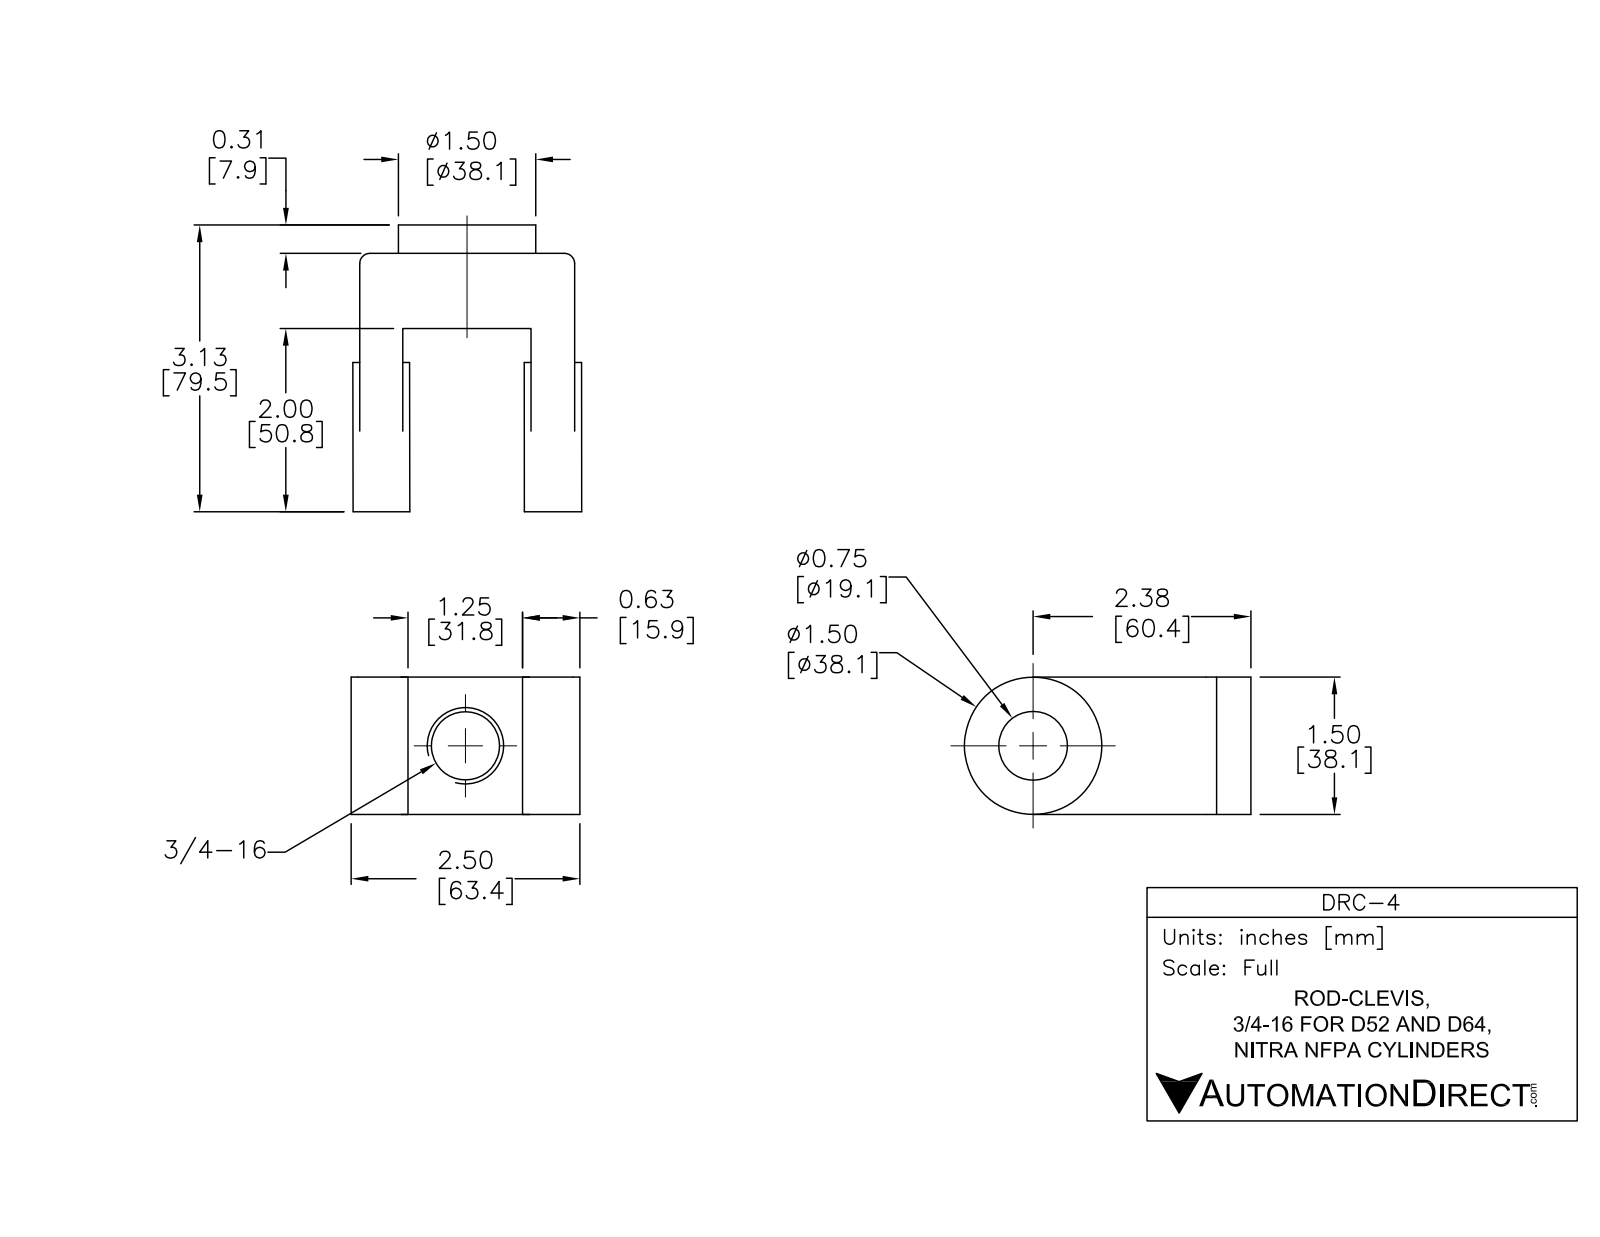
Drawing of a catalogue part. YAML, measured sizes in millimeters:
part_name: "DRC-4"
step_written_by: "SolidWorks 2015 (AUTOMOTIVE_DESIGN)"
units: millimeters
bodies: {solids: 1, faces: 28, planar: 14, cylindrical: 14, other: 0}
overall_size: [79.5, 63.5, 38.1]
volume: 94620
surface_area: 21500
round_holes:
  - {diameter: 17.4, count: 1}
  - {diameter: 19.1, count: 1}
round_bosses_or_shafts:
  - {diameter: 38.1, count: 2}
partial_cylinders:
  - {radius: 1.9, count: 2}
face_to_face_distances: [38.1, 1.3, 15.9, 47.6, 62.2, 14.6, 46.4, 61, 14.6, 48.9]
